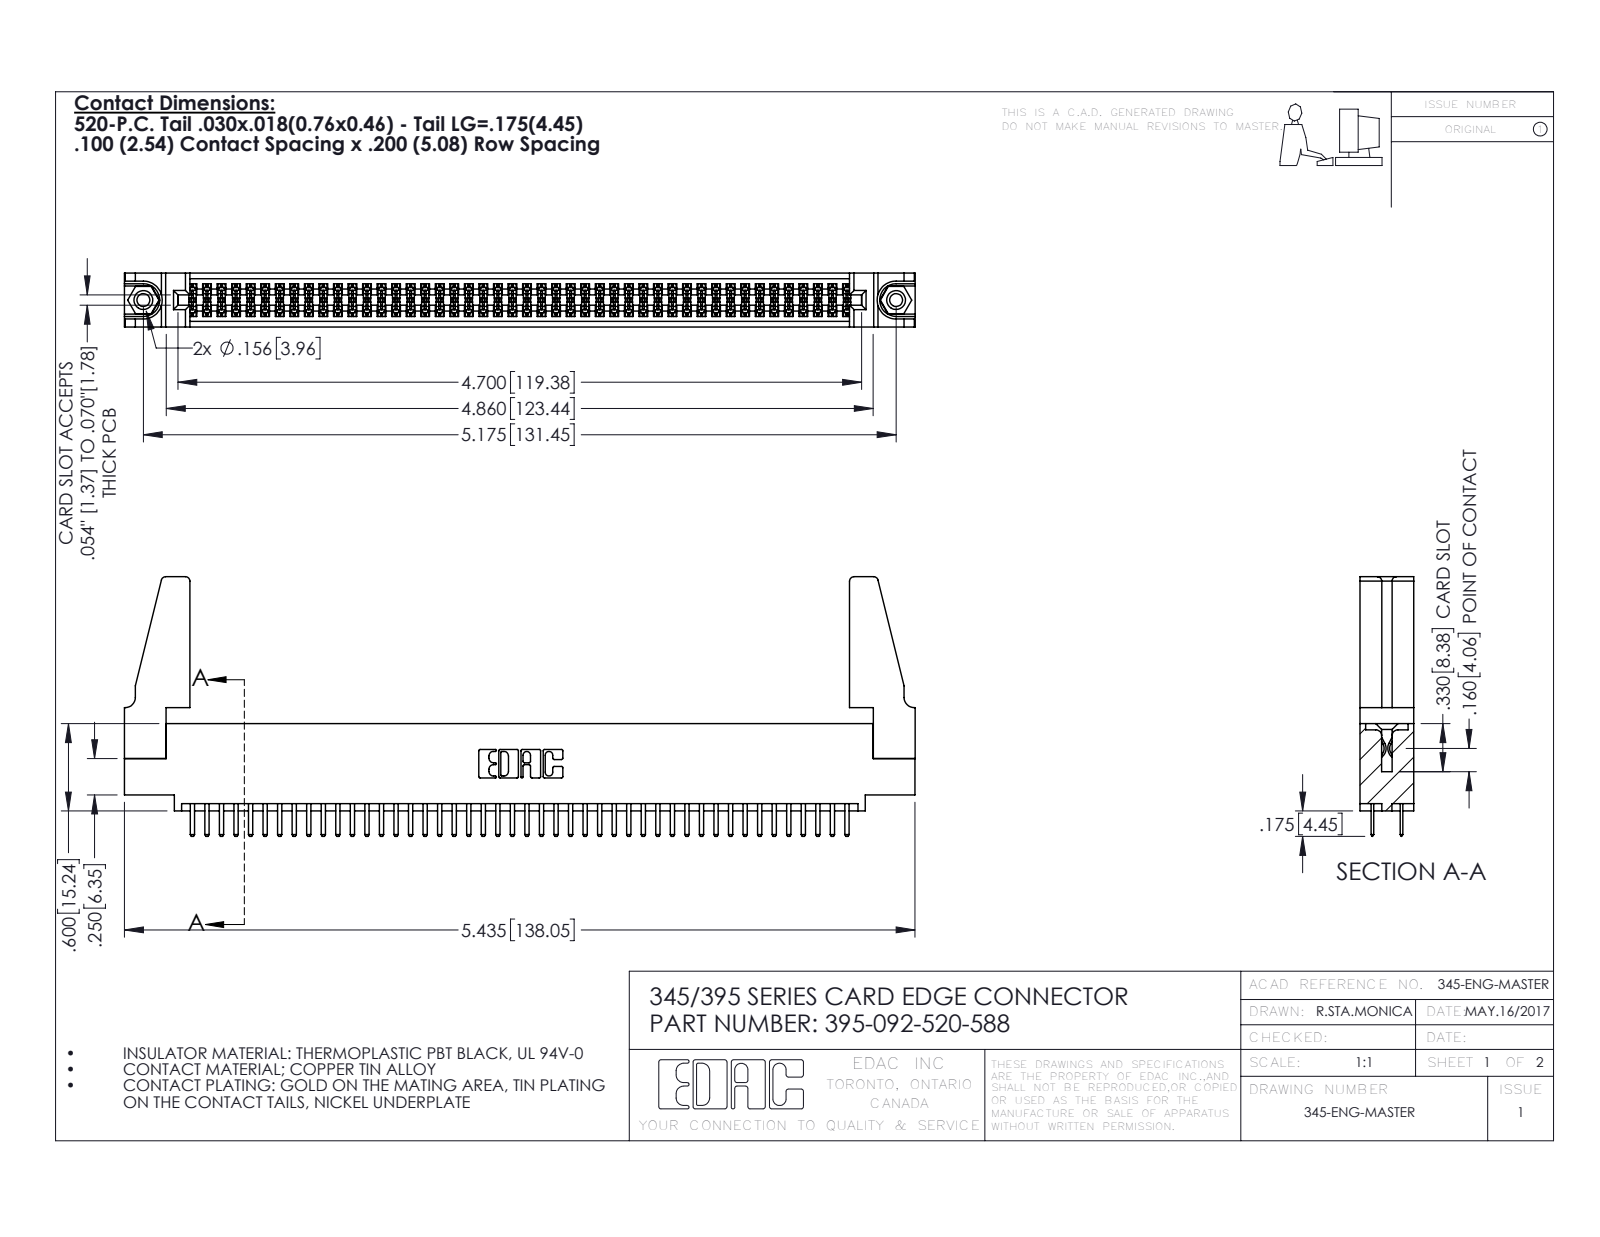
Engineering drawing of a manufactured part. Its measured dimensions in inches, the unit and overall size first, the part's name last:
Units: inches
Overall size (bounding box): 5.436 × 1.785 × 0.37
Round holes (diameter × count): ⌀0.089 ×2, ⌀0.125 ×2, ⌀0.156 ×2, ⌀0.064 ×1
Round bosses / shafts (diameter × count): ⌀0.155 ×2
Partial cylindrical surfaces — rounded edges, fillets, slot ends (radius × count): R0.006 ×138, R0.01 ×96, R0.01 ×22, R0.03 ×8, R0.007 ×6, R0.031 ×6, R0.026 ×3, R0.014 ×2
Main face-to-face distances: 0.072, 0.298, 0.37, 0.2, 0.098, 0.272, 0.025, 0.225, 0.022, 0.072
Hole centre spacings: 0.27, 4.939, 5.175
Volume: 1.012 in³ · Surface area: 35.52 in²
Bodies: 97 solids, 5222 faces (3376 planar, 1830 cylindrical, 16 other)
Part name (STEP PRODUCT): 345-250-001_345-250-001-102; 345-220-078_345-220-088; 345 Part_0.110 Offset - 0.156 Dia-TH; 395-092-520-588 (+1 more)
STEP written by: SolidWorks 2016 (CONFIG_CONTROL_DESIGN)
